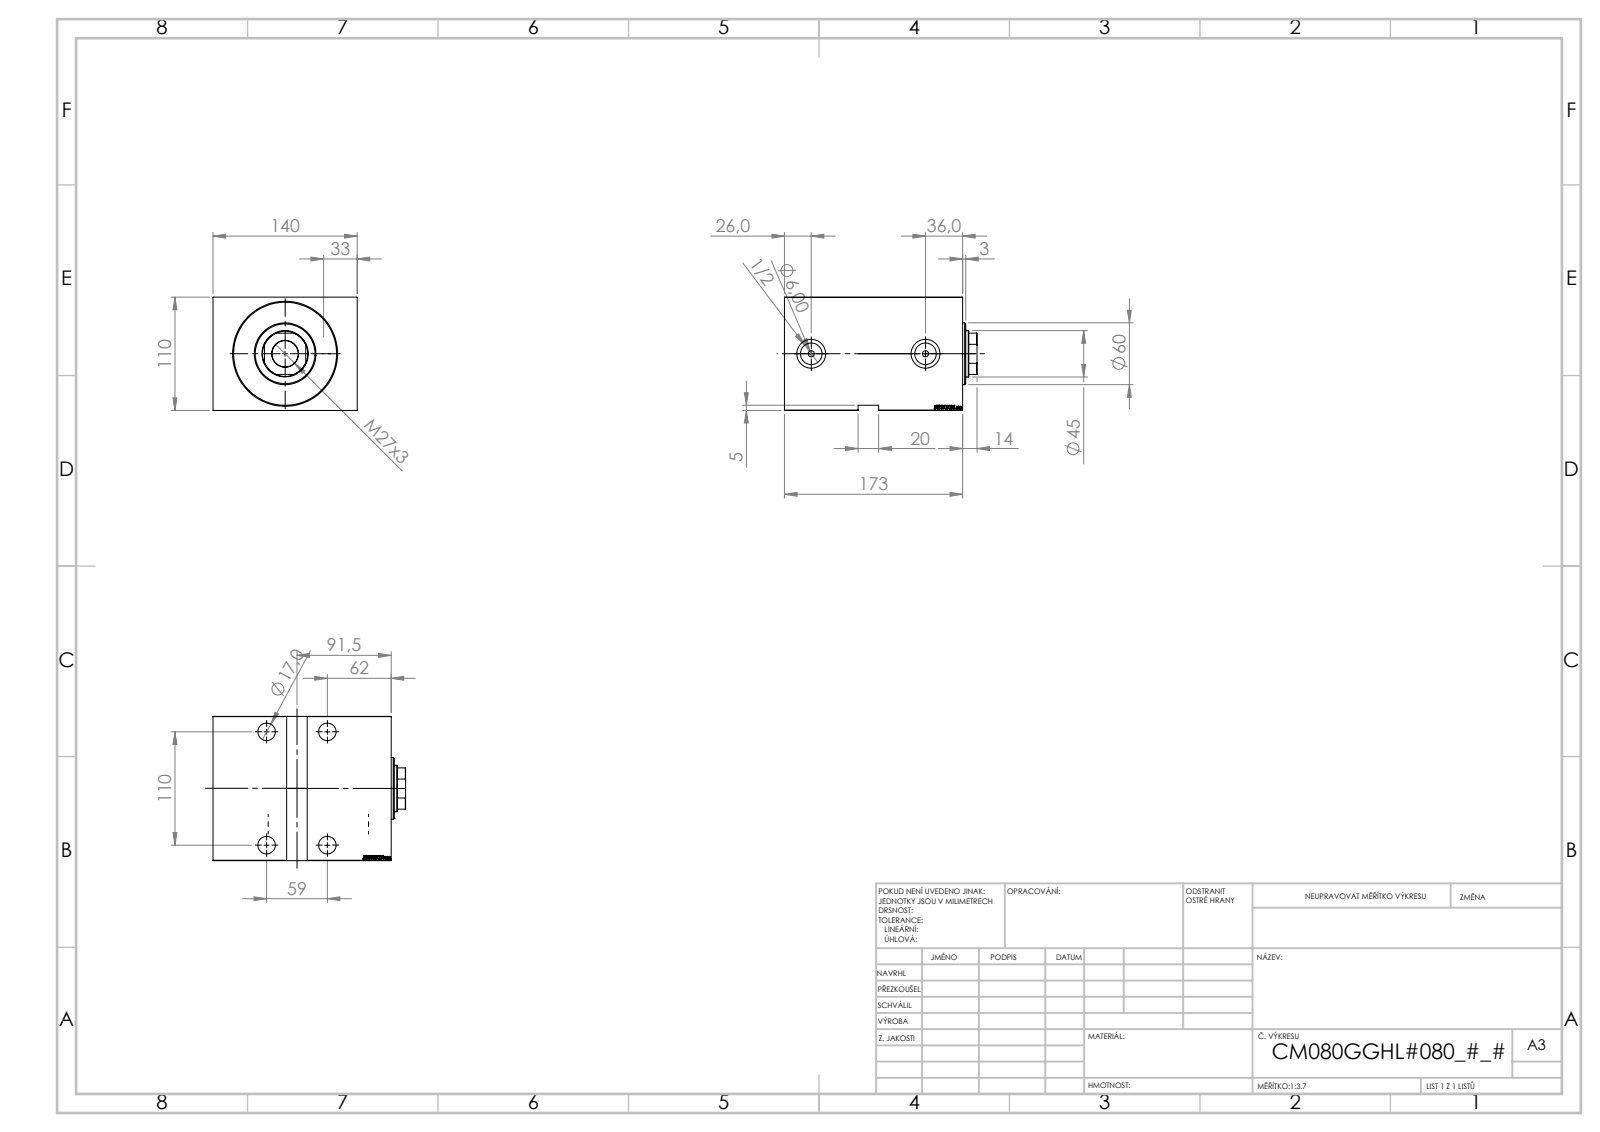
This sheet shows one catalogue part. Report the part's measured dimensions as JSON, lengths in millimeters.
{"part_name": "V450CM_G_VCP; V450CM_G_Body; Zatka_OIL_PORT; V450CM_VC_G", "step_written_by": "SolidWorks 2019 (CONFIG_CONTROL_DESIGN)", "units": "millimeters", "bodies": {"solids": 5, "faces": 891, "planar": 439, "cylindrical": 54, "other": 398}, "overall_size": [187, 140, 110], "volume_mm3": 2216000, "surface_area_mm2": 244660, "round_holes": [[17, 4], [25, 4], [6, 2], [20.96, 2], [28, 2], [25.5, 1], [45, 1], [80, 1], [82, 1], [100, 1]], "round_bosses_or_shafts": [[26, 2], [60, 1]], "partial_cylinders_radius": [[22, 1]], "face_to_face_distances": [110, 140, 5, 173, 21, 152, 168, 147, 79, 58], "hole_center_spacings": [59, 110, 124.82, 111]}
